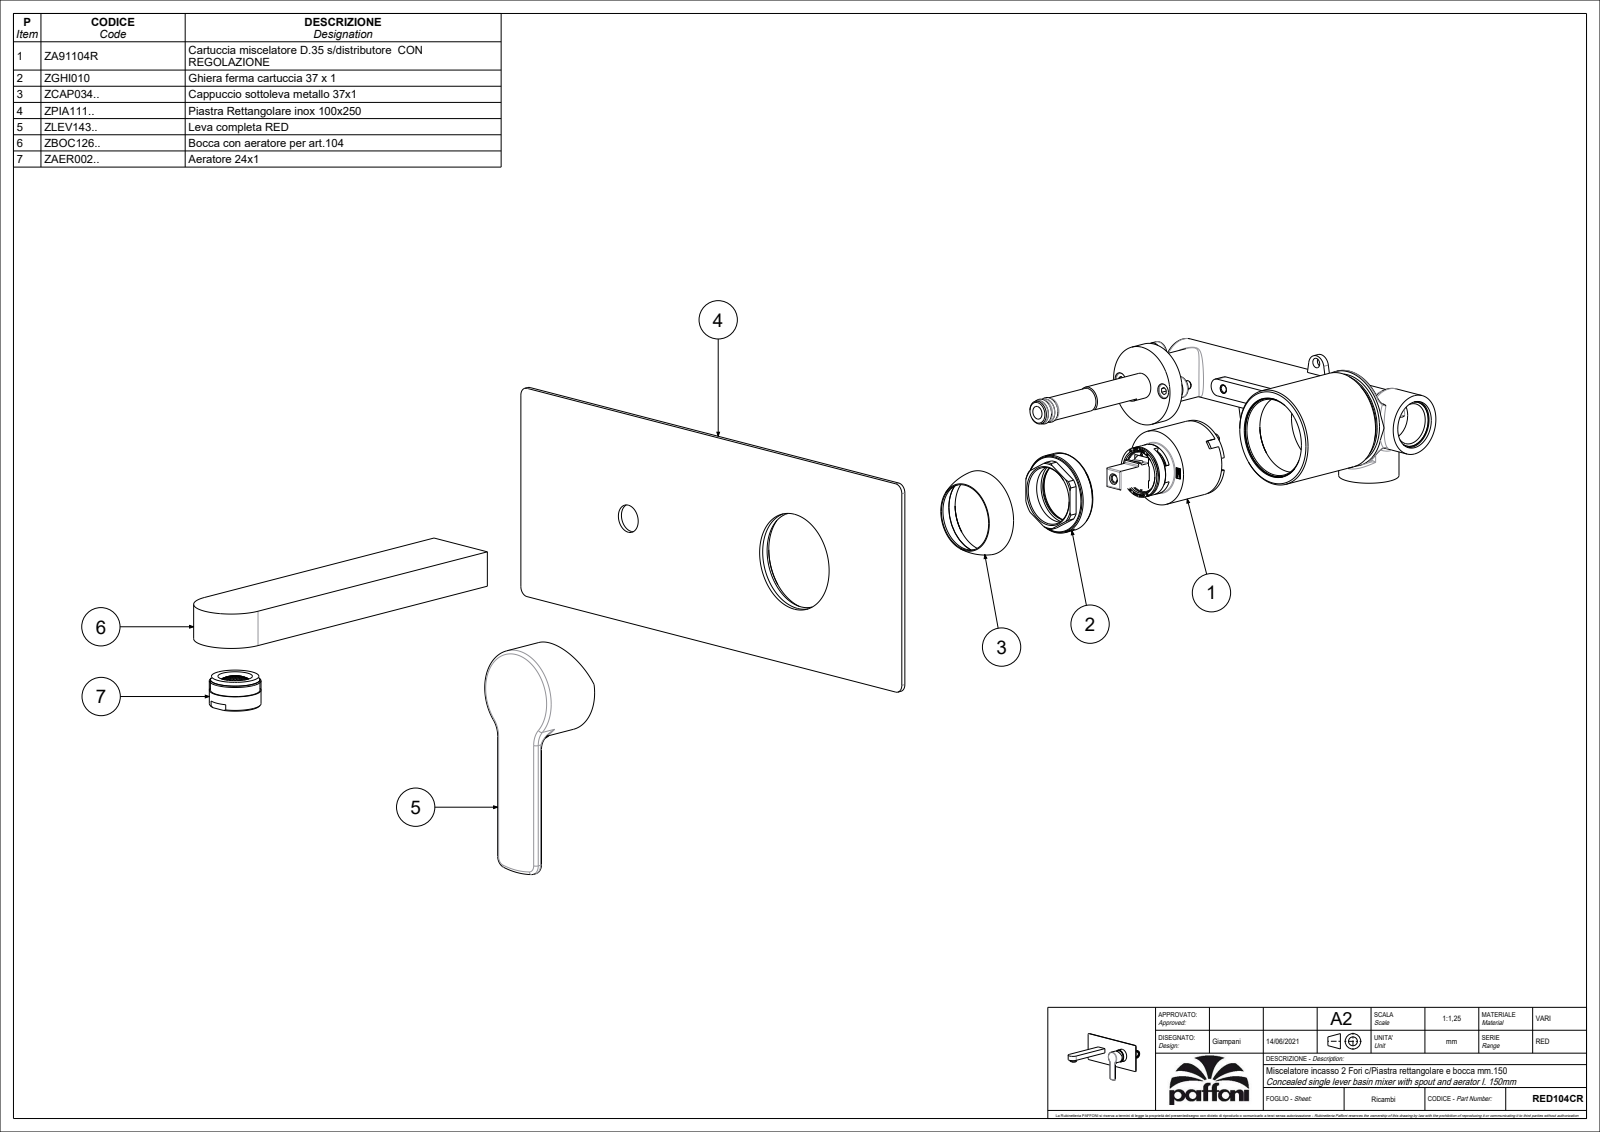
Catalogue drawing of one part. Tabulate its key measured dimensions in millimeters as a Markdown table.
| quantity | value |
| --- | --- |
| part name | RED104CR |
| STEP written by | CREO PARAMETRIC BY PTC INC, 2020044 (CONFIG_CONTROL_DESIGN) |
| units | millimeters |
| bodies | 4 solids, 2523 faces (2012 planar, 285 cylindrical, 226 other) |
| overall size | 250 × 170 × 135 |
| volume | 175 421 mm³ |
| surface area | 111 470 mm² |
| round holes (diameter × count) | 3.3 × 2, 4 × 2, 6 × 2, 3 × 1, 4.5 × 1, 5 × 1, 11 × 1, 12 × 1, 13 × 1, 15 × 1, 16 × 1, 17 × 1 |
| round bosses / shafts (diameter × count) | 44.8 × 1, 43 × 1, 35 × 1, 24 × 1, 23.5 × 1, 23.4 × 1, 21.8 × 1, 19.5 × 1 |
| partial cylindrical surfaces (radius × count) | 0.5 × 45, 0.15 × 11, 0.3 × 4, 1.5 × 4, 4 × 4, 1 × 2, 2.1 × 2, 2.5 × 2 |
| main face-to-face distances | 2, 16.5, 35, 50.1, 48.1, 4.5, 54.6, 52.6, 41.75, 58.25 |
| hole center spacings | 2.5, 12.5, 109, 109.03, 155.86, 165.02 |
